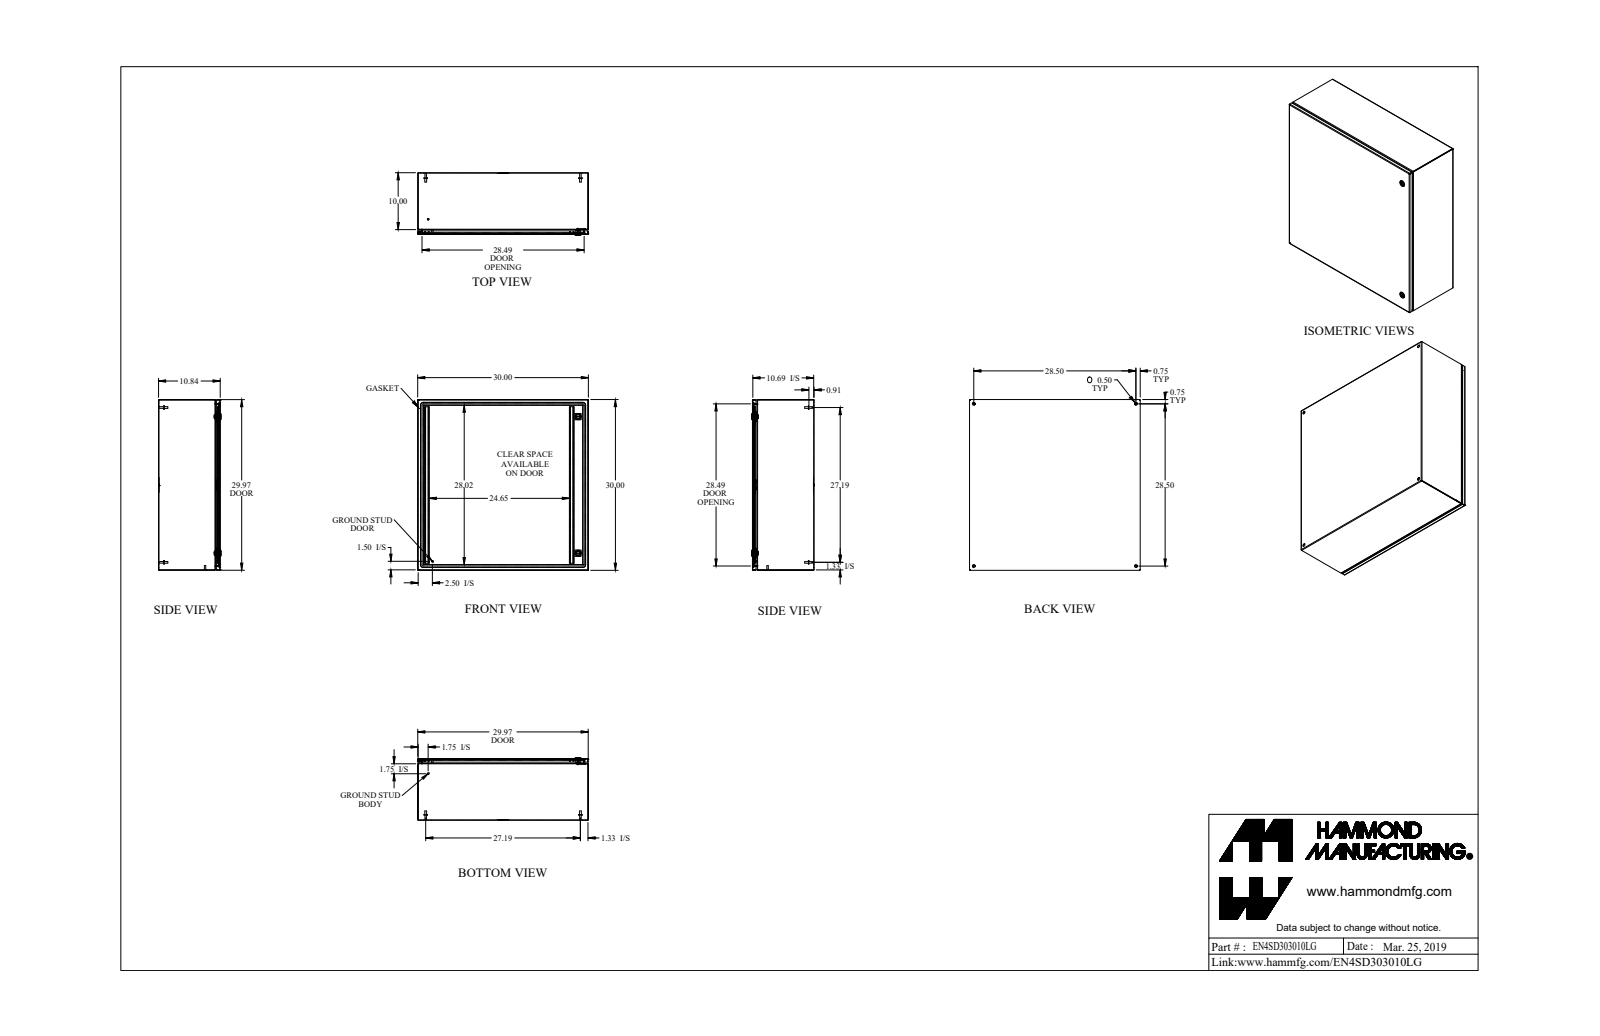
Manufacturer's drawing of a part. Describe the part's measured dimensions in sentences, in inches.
The part is named "EN4SD303010LG". Its 3-D file was written by "SolidWorks 2019 (AUTOMOTIVE_DESIGN)". It is 31 solids with 854 faces: 395 planar, 295 cylindrical and 164 other. Overall it measures 30 by 30 by 10.997 inches. Its volume is 248.1 cubic inches and its surface area 6 948 square inches. Round holes: 4 of diameter 0.5, 2 of diameter 0.232, 2 of diameter 0.625, 2 of diameter 0.785, 1 of diameter 0.172, 1 of diameter 0.24, 1 of diameter 0.242. Round bosses or shafts: 4 of diameter 0.625, 4 of diameter 0.313, 4 of diameter 0.27, 2 of diameter 1.1, 2 of diameter 0.525, 2 of diameter 0.281, 2 of diameter 0.25, 1 of diameter 0.455. Partial cylindrical surfaces (rounded edges, fillets, slot ends): 24 of radius 0.108, 16 of radius 0.036, 12 of radius 0.043, 12 of radius 0.081, 12 of radius 0.382, 8 of radius 19.003, 6 of radius 0.006, 6 of radius 0.062. The main face-to-face distances are 0.072, 10.765, 29.928, 10.693, 10.837, 29.856, 30, 0.837, 9.928, 0.75. The hole center spacings are 28.5, 2.493, 26.272, 27.519, 37.964, 40.305, 23.999.
